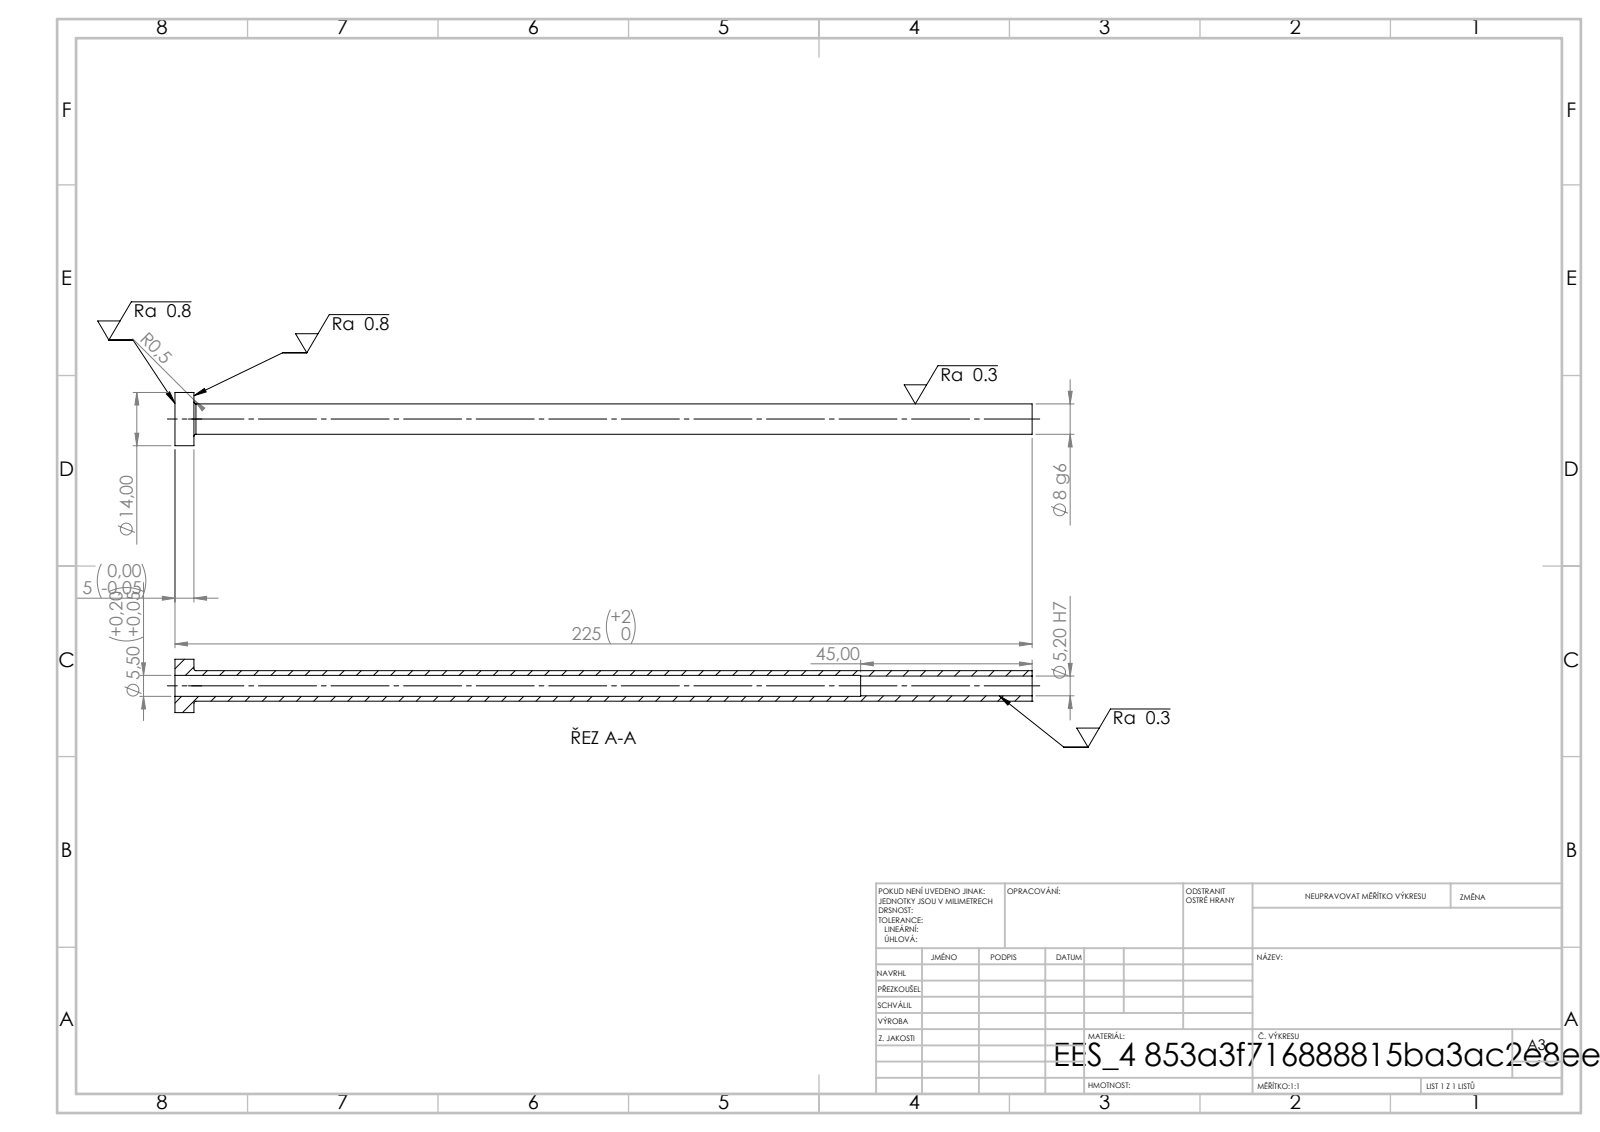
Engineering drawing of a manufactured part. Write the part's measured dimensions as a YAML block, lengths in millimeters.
step_written_by: "SolidWorks 2019 (CONFIG_CONTROL_DESIGN)"
units: millimeters
bodies: {solids: 1, faces: 14, planar: 4, cylindrical: 8, other: 2}
overall_size: [225, 14, 14]
volume: 6597
surface_area: 9855
round_holes:
  - {diameter: 5.2, count: 1}
  - {diameter: 5.5, count: 1}
round_bosses_or_shafts:
  - {diameter: 14, count: 1}
  - {diameter: 8, count: 1}
face_to_face_distances: [5, 225, 220, 180, 175, 45]
